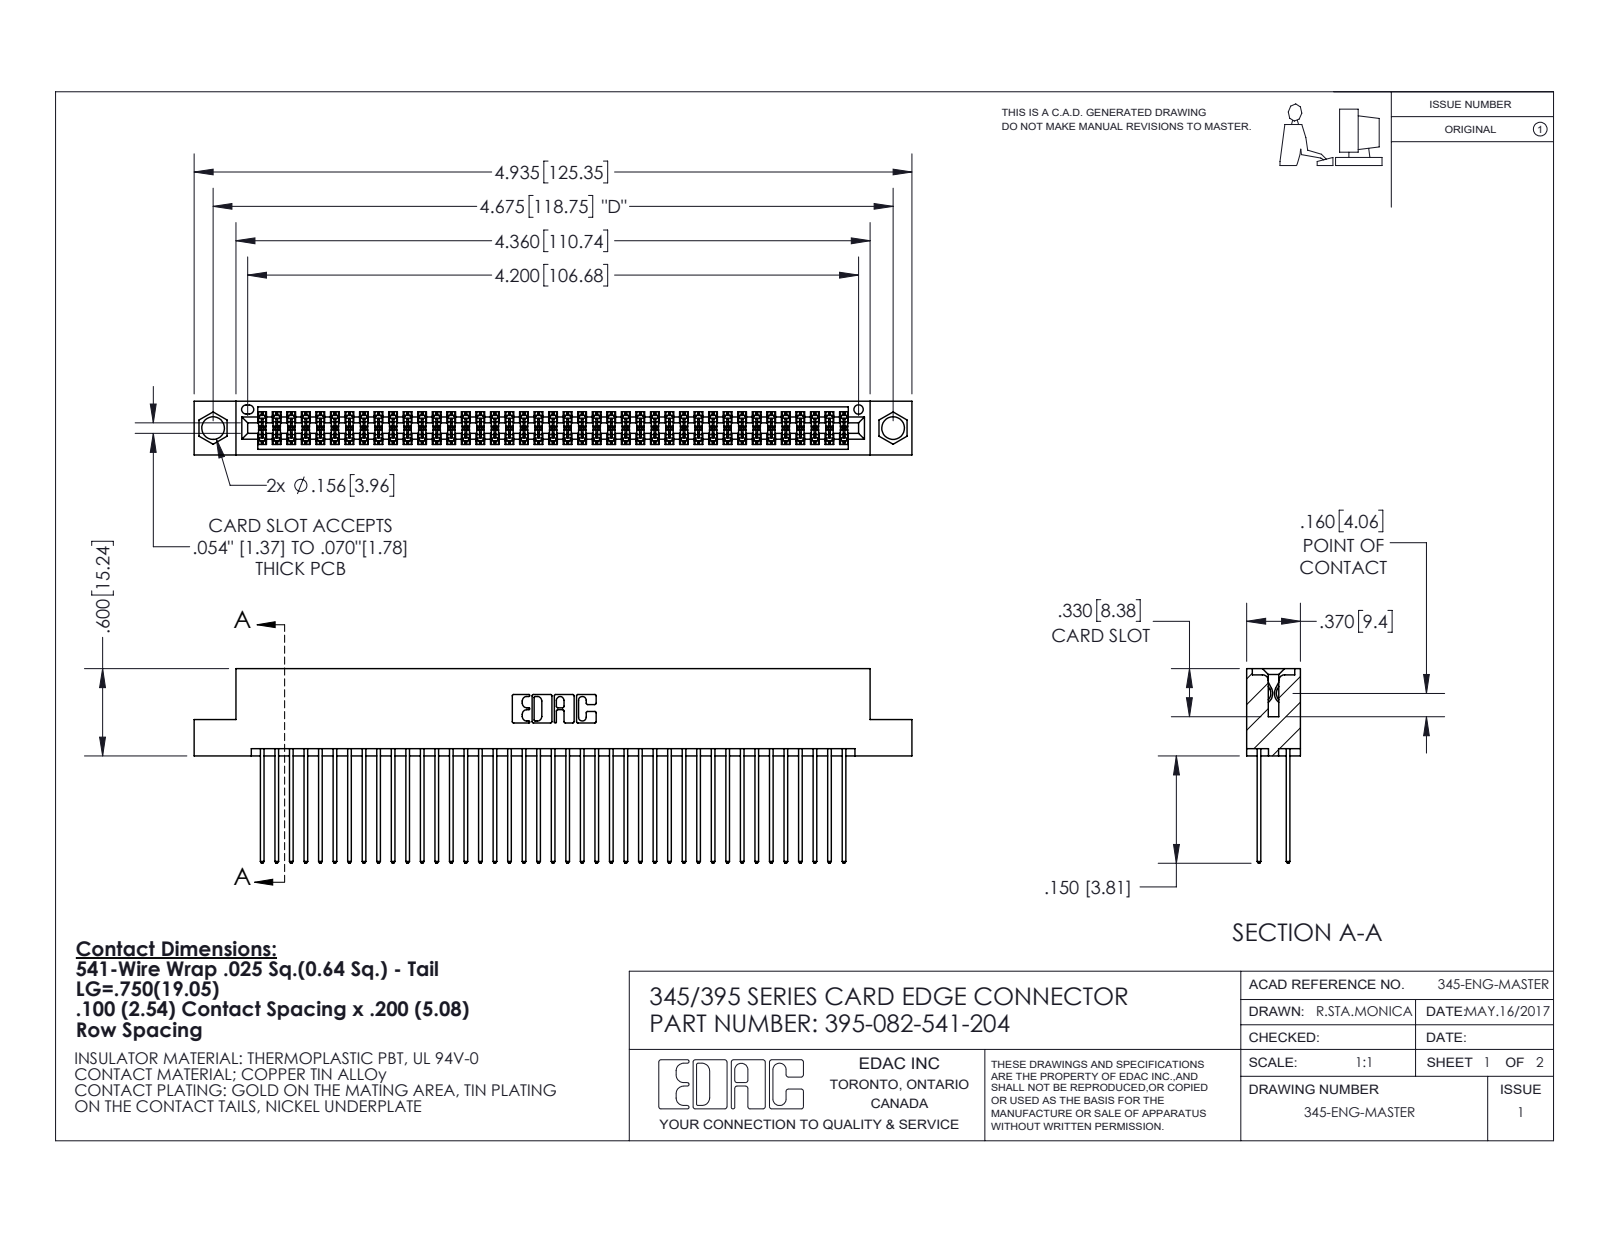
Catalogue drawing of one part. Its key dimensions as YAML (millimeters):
part_name: "395-082-541-204; 345 Part_Flush Mounting Lugs - 0.156 Dia-TI; 345-292-001_345-293-141"
step_written_by: "SolidWorks 2020 (CONFIG_CONTROL_DESIGN)"
units: millimeters
bodies: {solids: 83, faces: 4240, planar: 2800, cylindrical: 1440, other: 0}
overall_size: [125.3, 34, 9.4]
volume: 12500
surface_area: 20570
round_holes:
  - {diameter: 4, count: 2}
  - {diameter: 1.6, count: 1}
partial_cylinders:
  - {radius: 0.2, count: 163}
  - {radius: 0.3, count: 82}
  - {radius: 0.3, count: 22}
  - {radius: 0.2, count: 6}
  - {radius: 0.8, count: 6}
  - {radius: 0.7, count: 3}
  - {radius: 0.4, count: 2}
  - {radius: 0.5, count: 2}
face_to_face_distances: [1.8, 7.6, 5.1, 2.5, 6.9, 0.6, 5.7, 9.4, 4.4, 3.8]
hole_center_spacings: [6.9, 112.8, 118.7]
